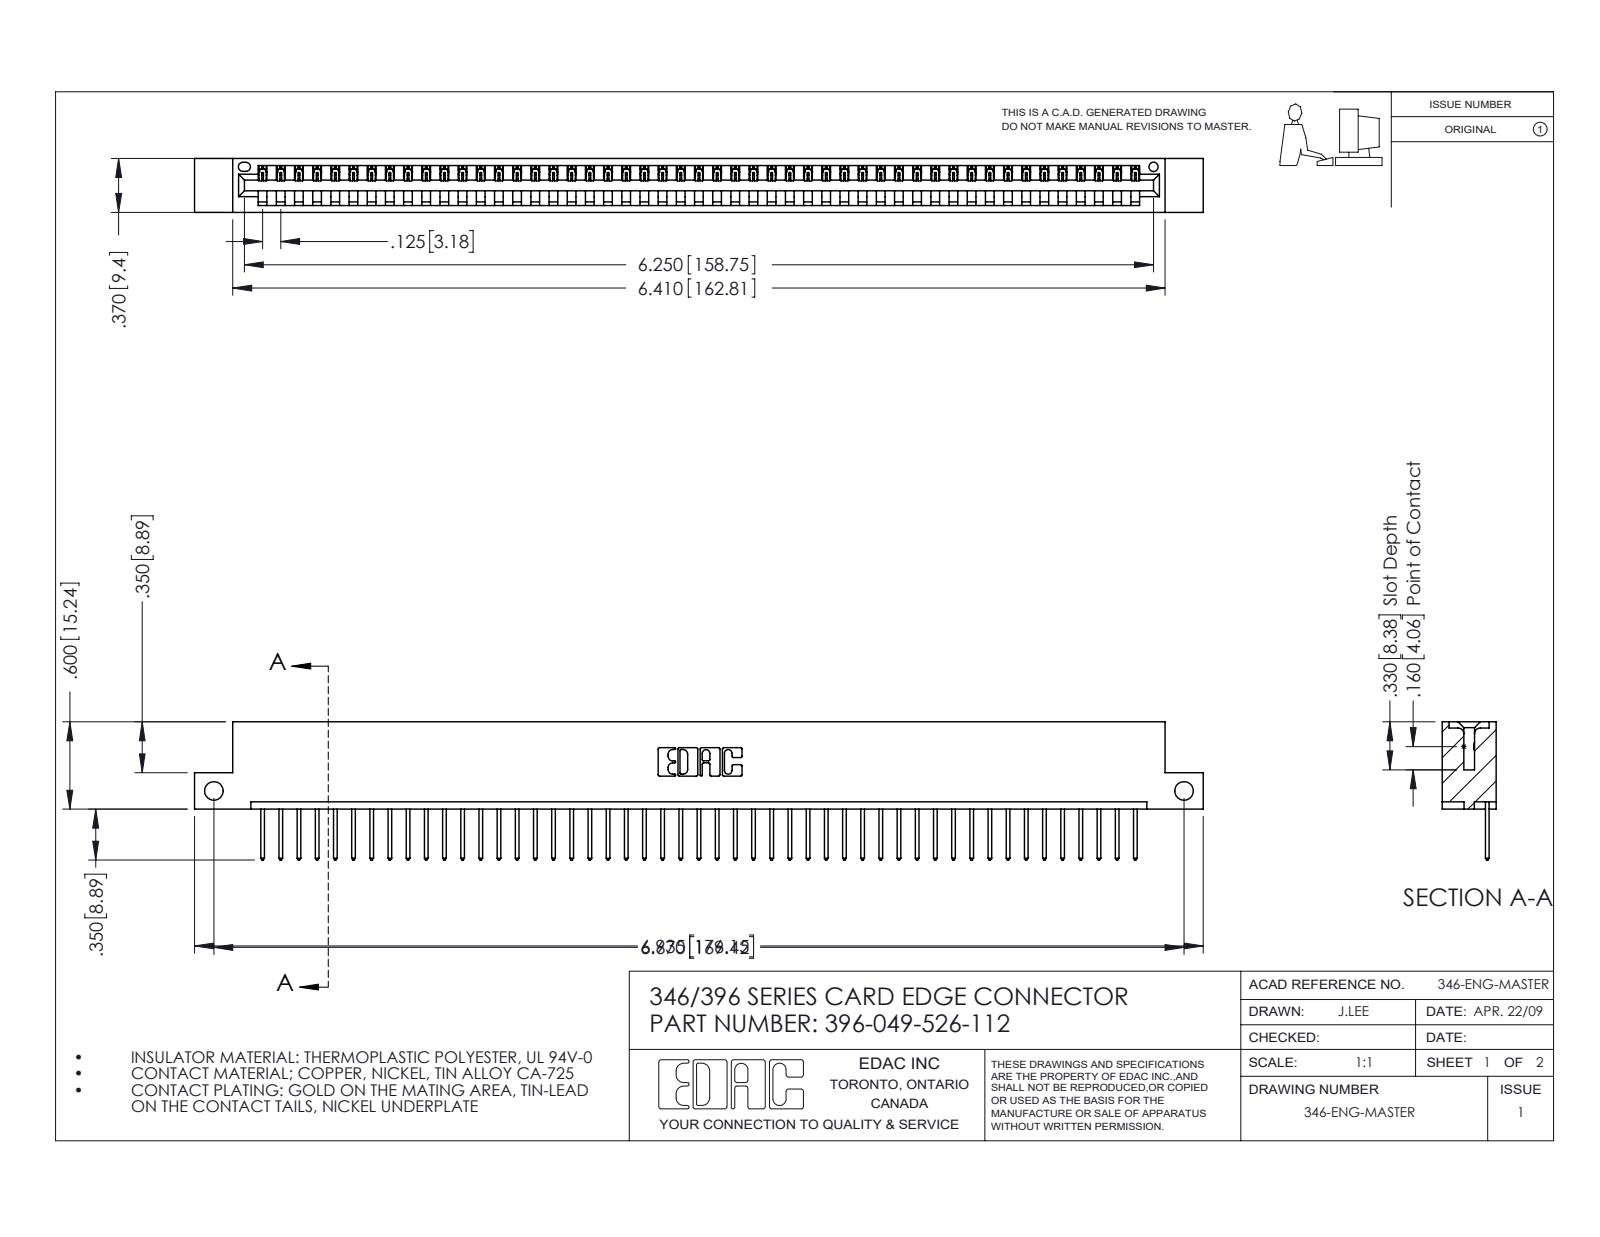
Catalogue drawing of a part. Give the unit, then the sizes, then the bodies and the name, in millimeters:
Units: millimetres
Overall size (bounding box): 176.1 × 24.1 × 9.4
Round holes (diameter × count): ⌀3.3 ×2, ⌀1.6 ×1
Partial cylindrical surfaces — rounded edges, fillets, slot ends (radius × count): R0.2 ×98, R0.3 ×98, R0.3 ×22, R0.2 ×6, R0.8 ×6, R0.7 ×3, R0.8 ×2, R1 ×2
Main face-to-face distances: 1.2, 8.2, 9.4, 6.4, 1.8, 7.6, 0.6, 3.8, 5.6, 2.5
Hole centre spacings: 169.4
Volume: 16 780 mm³ · Surface area: 20 860 mm²
Bodies: 50 solids, 2964 faces (2036 planar, 928 cylindrical, 0 other)
Part name (STEP PRODUCT): 345-292-001_345-293-126; 346 Part_Flush Mounting Lugs - Side Mount; 396-049-526-112
STEP written by: SolidWorks 2016 (CONFIG_CONTROL_DESIGN)
